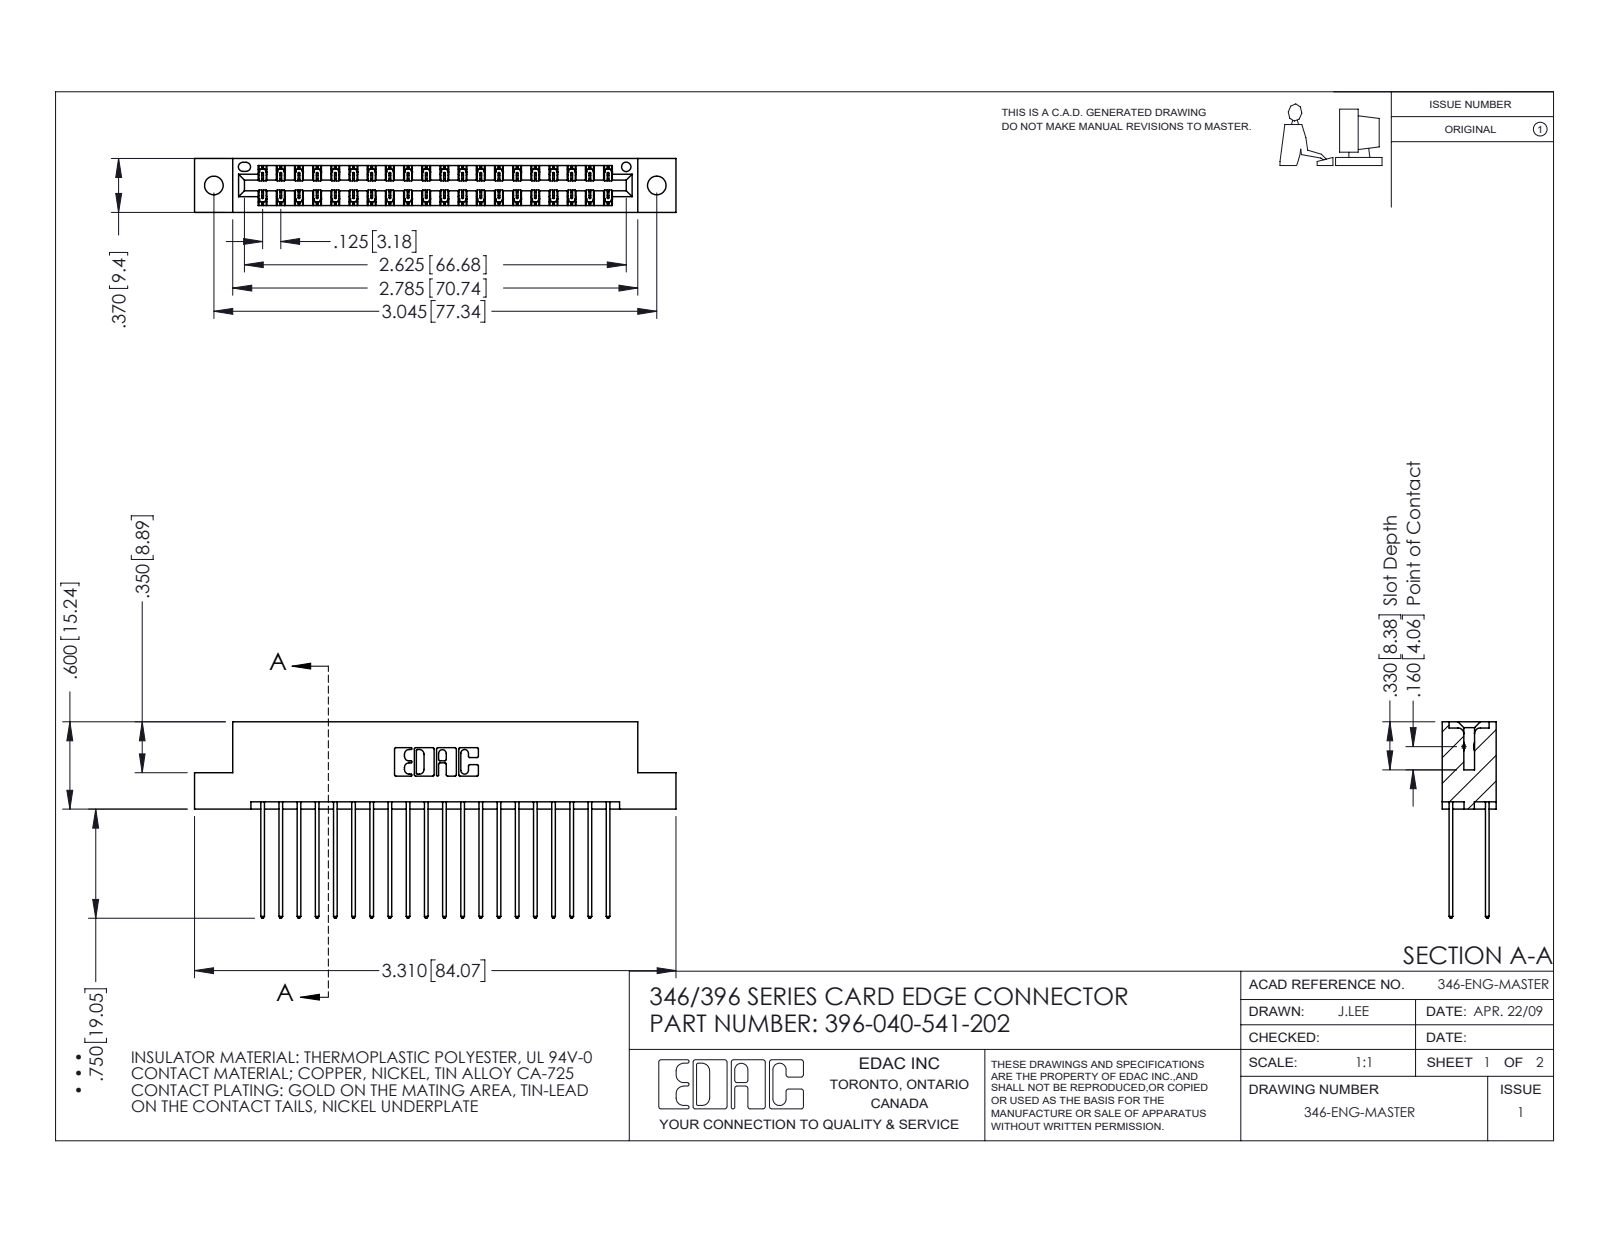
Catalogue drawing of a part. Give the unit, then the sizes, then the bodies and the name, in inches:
Units: inches
Overall size (bounding box): 3.31 × 1.35 × 0.37
Round holes (diameter × count): ⌀0.128 ×2, ⌀0.064 ×1
Partial cylindrical surfaces — rounded edges, fillets, slot ends (radius × count): R0.006 ×60, R0.01 ×40, R0.01 ×22, R0.007 ×6, R0.031 ×6, R0.026 ×3, R0.014 ×2, R0.022 ×2
Main face-to-face distances: 0.048, 0.322, 0.25, 0.072, 0.298, 0.025, 0.37, 0.275, 0.148, 0.222
Hole centre spacings: 0.246, 2.837, 3.045
Volume: 0.502 in³ · Surface area: 18.27 in²
Bodies: 41 solids, 2202 faces (1476 planar, 726 cylindrical, 0 other)
Part name (STEP PRODUCT): 396-040-541-202; 345-292-001_345-293-141; 346 Part_Flush Mounting Lugs - 0.128 Dia
STEP written by: SolidWorks 2016 (CONFIG_CONTROL_DESIGN)
